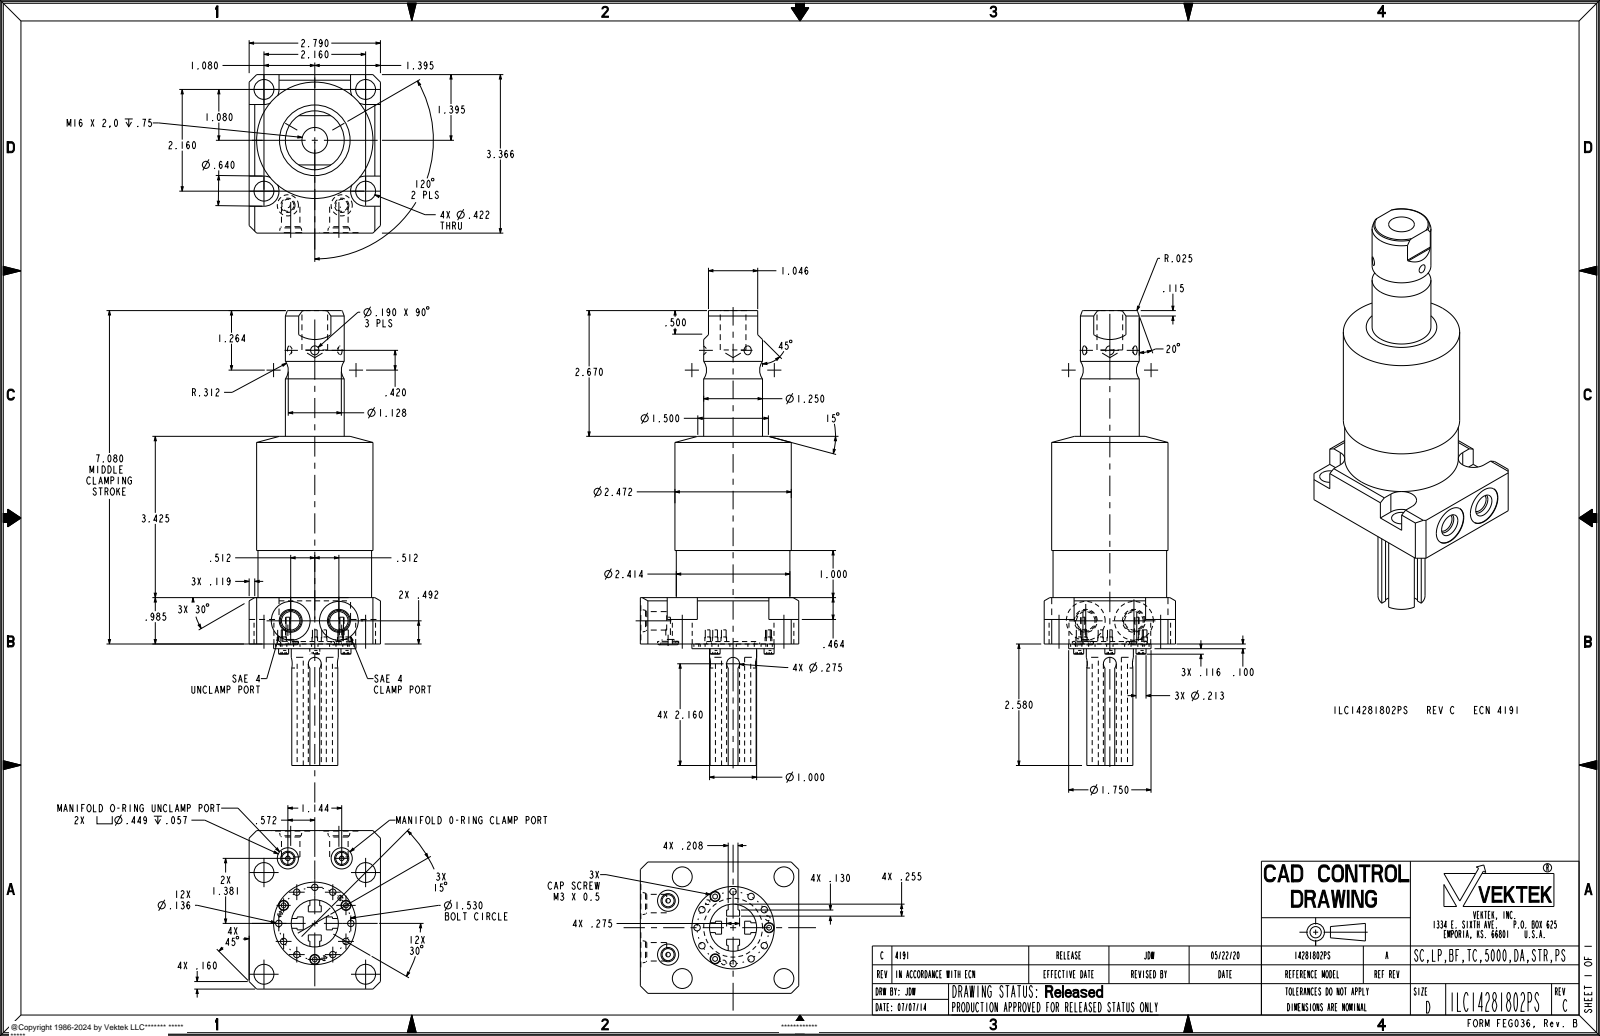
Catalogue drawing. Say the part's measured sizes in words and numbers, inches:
The part is named "ILC14281802PS". Its 3-D file was written by "PRO/ENGINEER BY PARAMETRIC TECHNOLOGY CORPORATION, 2013320 (AUTOMOTIVE_DESIGN)". It is 1 solid with 283 faces: 133 planar, 112 cylindrical and 38 other. Overall it measures 9.66 by 3.366 by 2.79 inches. Its volume is 28.58 cubic inches and its surface area 89.45 square inches. Round holes: 12 of diameter 0.136, 6 of diameter 0.1, 4 of diameter 0.422, 2 of diameter 0.098, 2 of diameter 0.256, 2 of diameter 0.392, 2 of diameter 0.449, 2 of diameter 0.825, 1 of diameter 0.546, 1 of diameter 1.13. Round bosses or shafts: 6 of diameter 0.118, 3 of diameter 0.213, 1 of diameter 2.472, 1 of diameter 2.414, 1 of diameter 1.75, 1 of diameter 1.25, 1 of diameter 1, 1 of diameter 0.917. Partial cylindrical surfaces (rounded edges, fillets, slot ends): 4 of radius 0.32, 2 of radius 0.03, 2 of radius 0.138. The main face-to-face distances are 0.985, 2.79, 0.107, 0.382, 0.141, 0.349, 0.033, 0.241, 1.64, 1.15. The hole center spacings are 0.765, 1.325, 0.396, 0.765, 0.813, 1.082, 1.125, 1.478.
